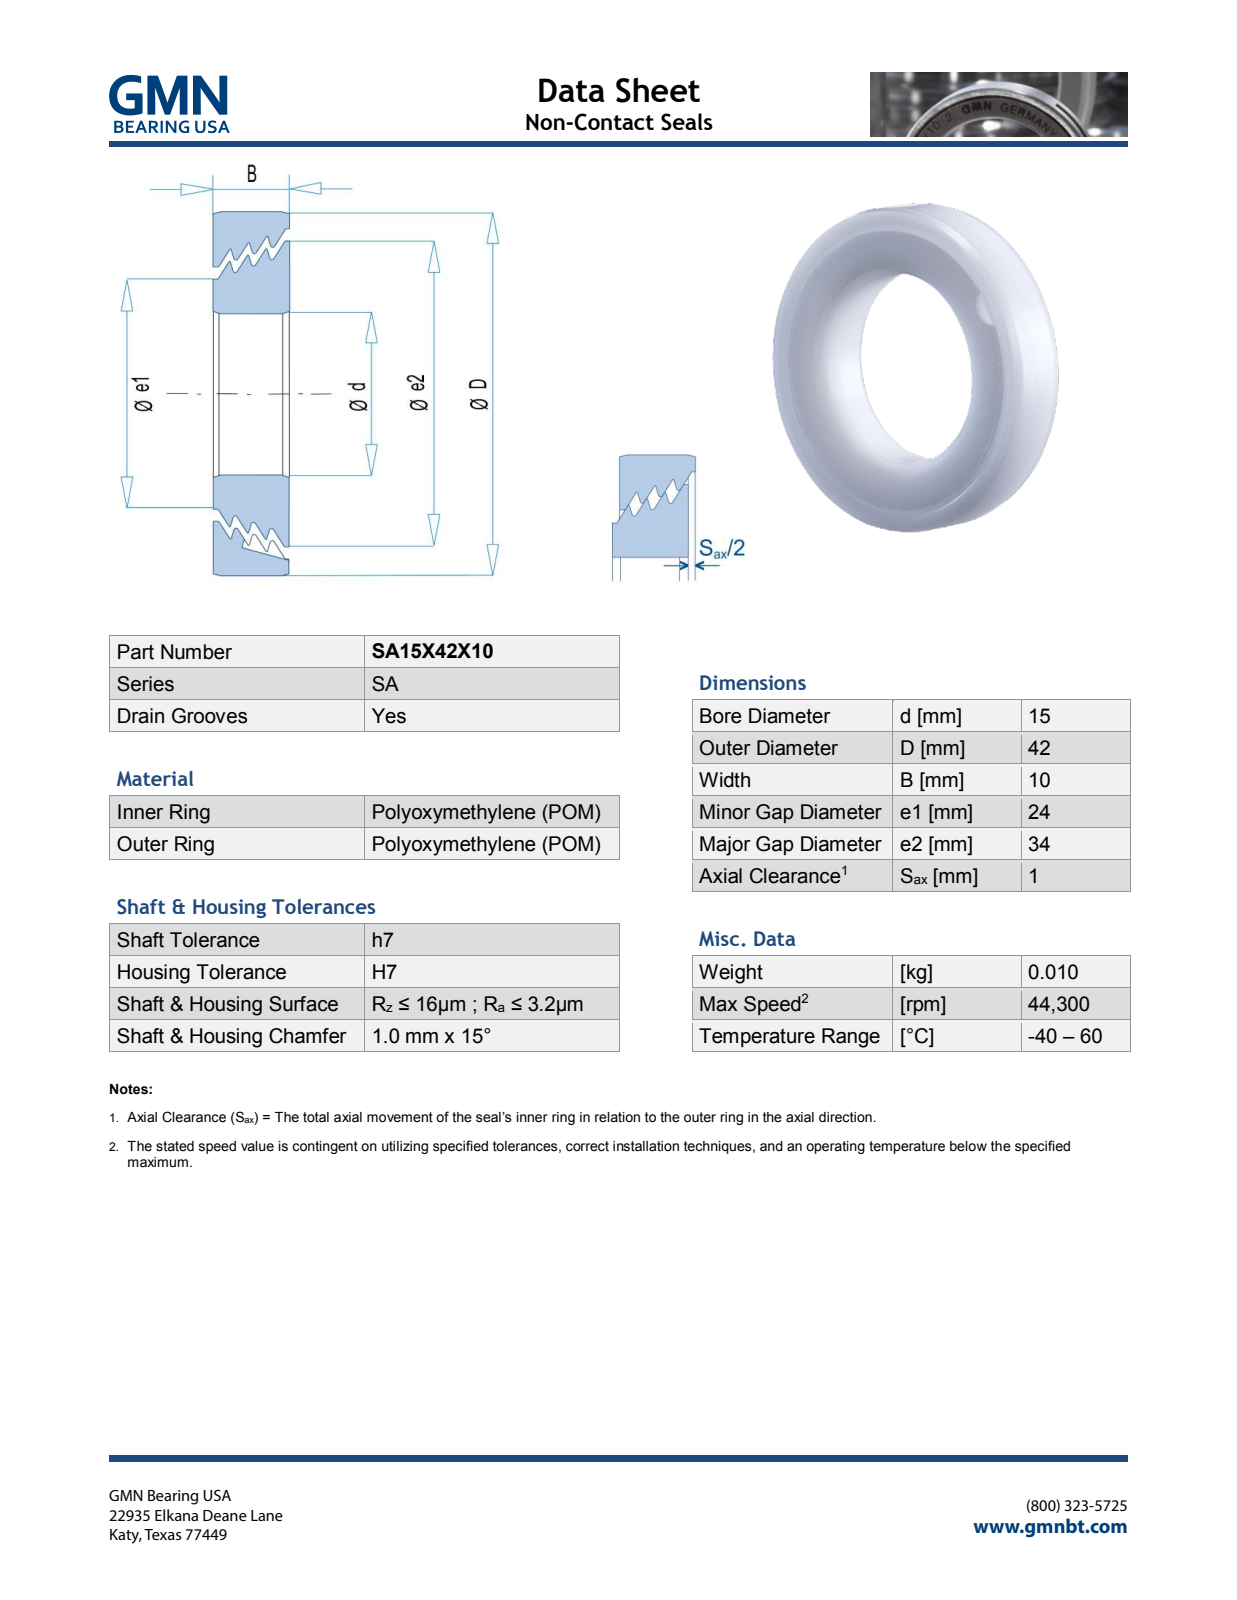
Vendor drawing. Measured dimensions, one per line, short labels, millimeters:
name: SA15X42X10_PRT
written by: PRO/ENGINEER BY PARAMETRIC TECHNOLOGY CORPORATION, 2013150 (AUTOMOTIVE_DESIGN)
unit: mm
bodies: 2 solids, 598 faces (521 planar, 15 cylindrical, 62 other)
size: 42 × 42 × 10.07
volume: 11 241 mm³; area: 7 815 mm²
holes: 1× ⌀15, 1× ⌀25.63, 1× ⌀35.63
bosses: 1× ⌀42, 1× ⌀34, 1× ⌀24
rounds: 1× R6
face distances: 10, 10.07, 0.32, 2.58, 0.33, 2.26, 2.25, 1.83, 2.15, 1.15
